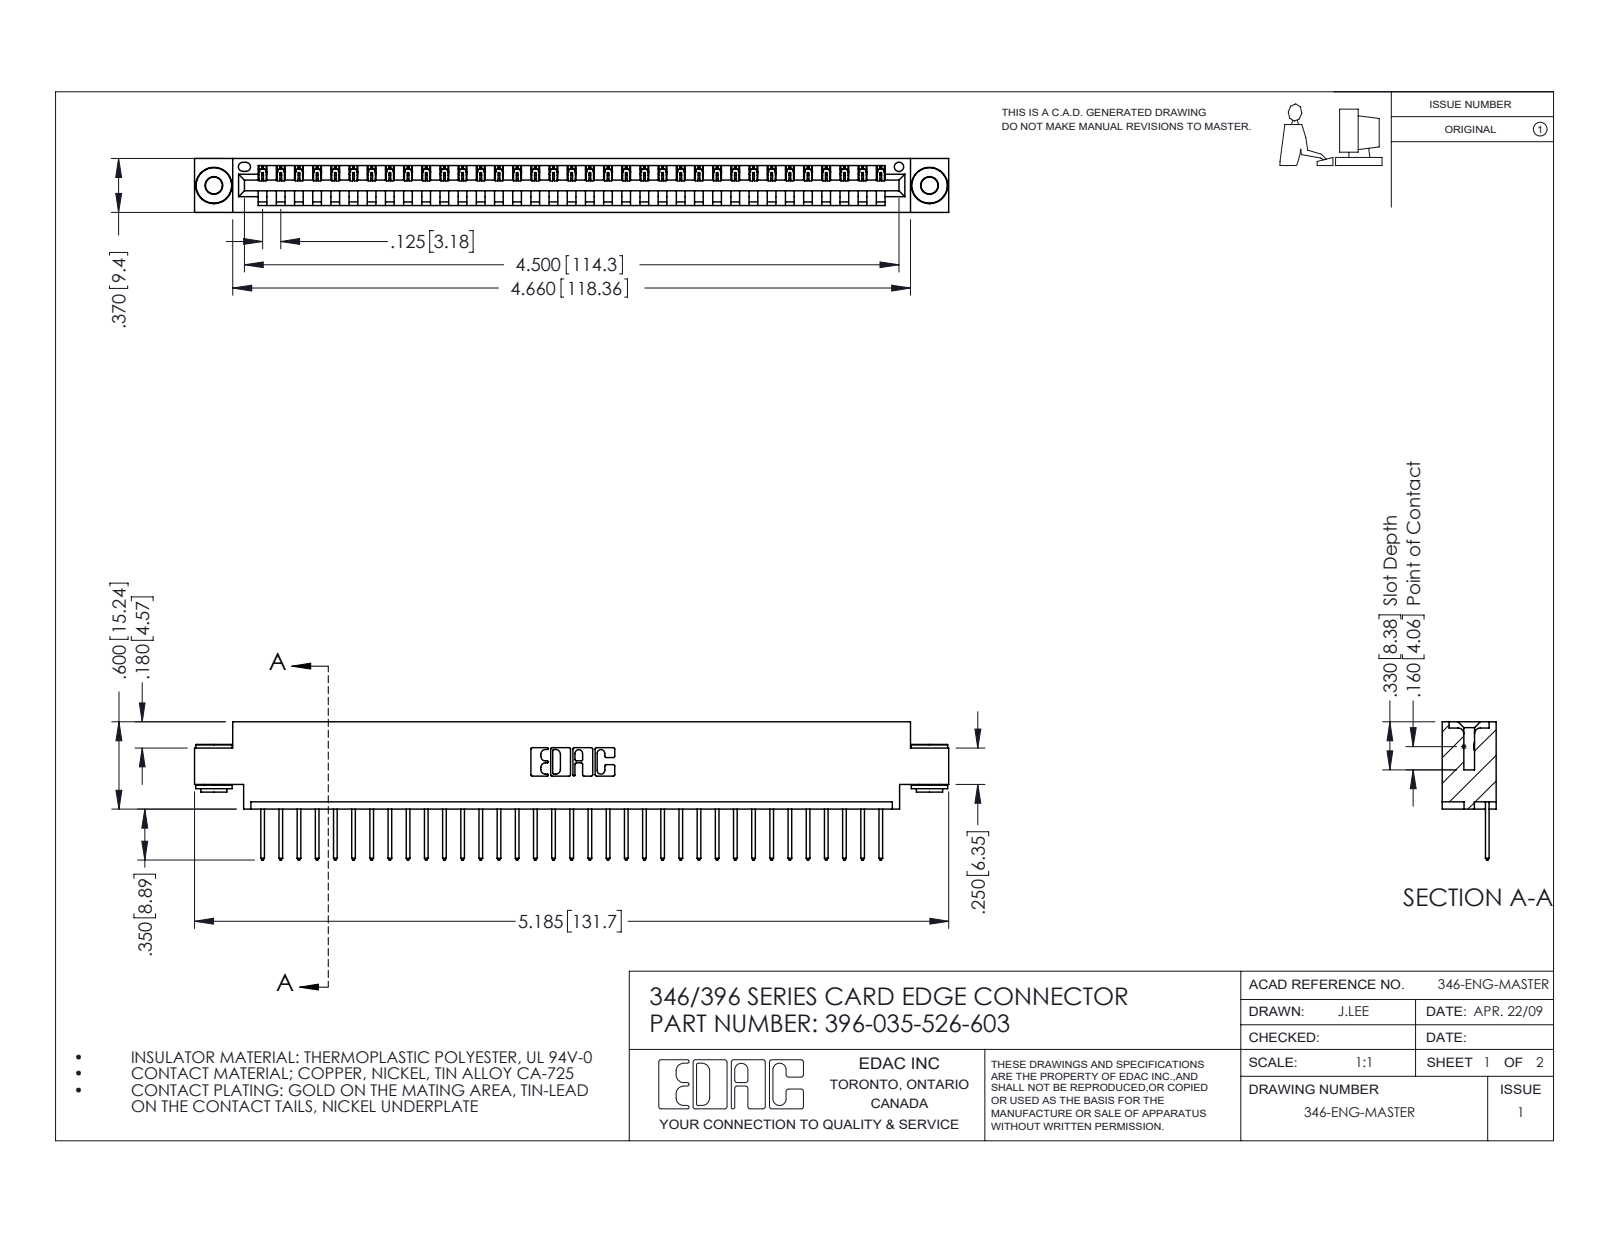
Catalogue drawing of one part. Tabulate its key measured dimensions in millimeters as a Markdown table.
| quantity | value |
| --- | --- |
| part name | 345-292-001_345-293-126; 396-035-526-603; 346 Part_0.170 Offset - 0.156 Dia-TH; 345-250-002_345-250-002-102 |
| STEP written by | SolidWorks 2016 (CONFIG_CONTROL_DESIGN) |
| units | millimeters |
| bodies | 38 solids, 2194 faces (1490 planar, 696 cylindrical, 8 other) |
| overall size | 131.7 × 24.1 × 9.4 |
| volume | 12 400 mm³ |
| surface area | 15 760 mm² |
| round holes (diameter × count) | 2.9 × 2, 4 × 2, 1.6 × 1 |
| round bosses / shafts (diameter × count) | 6.4 × 2, 4.6 × 2, 3.5 × 2 |
| partial cylindrical surfaces (radius × count) | 0.2 × 70, 0.3 × 70, 0.3 × 22, 0.2 × 6, 0.8 × 6, 0.7 × 3, 0.8 × 2, 1 × 2 |
| main face-to-face distances | 1.2, 8.2, 9.4, 6.4, 0.6, 1.8, 7.6, 3.8, 5.6, 2.5 |
| hole center spacings | 6.2, 119.7, 125 |
